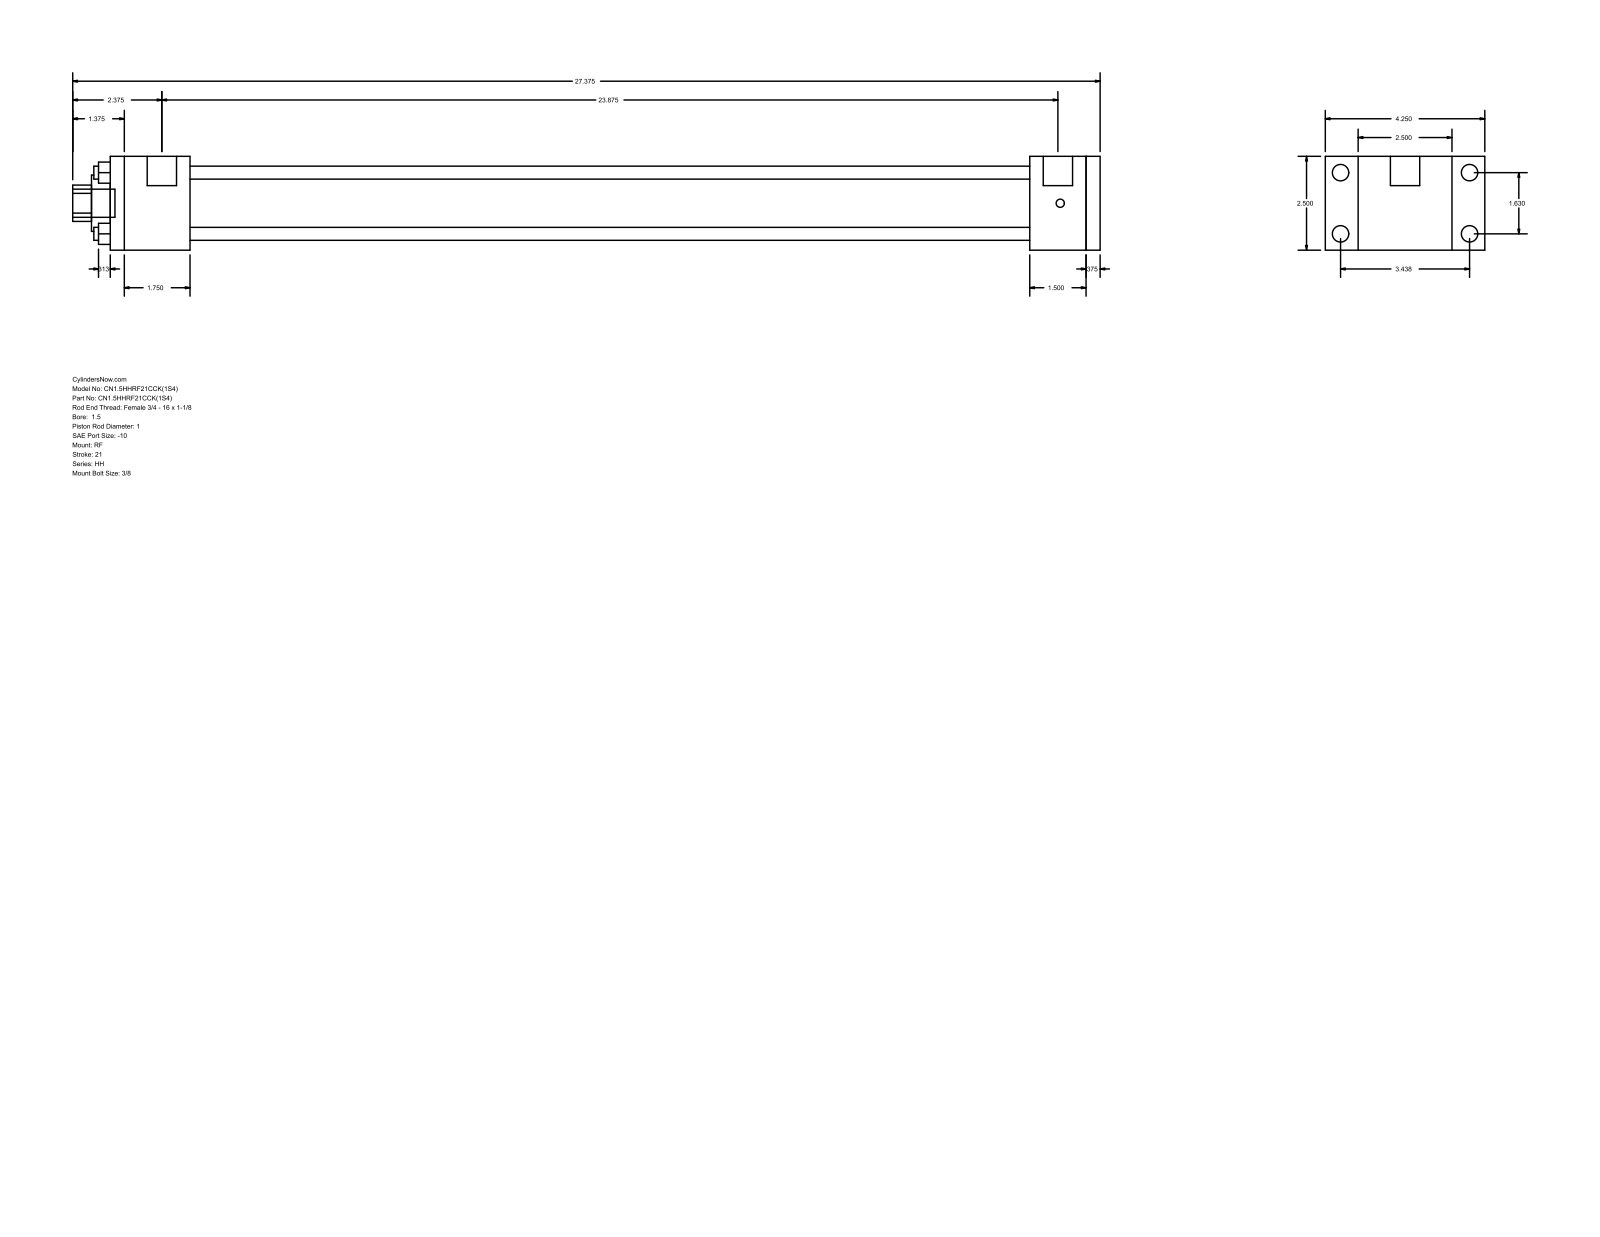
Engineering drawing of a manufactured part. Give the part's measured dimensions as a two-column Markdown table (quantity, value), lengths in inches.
| quantity | value |
| --- | --- |
| part name | HH_RF__0150_1 |
| STEP written by | GSSL Pune (CONFIG_CONTROL_DESIGN) |
| units | inches |
| bodies | 0 solids, 92 faces (64 planar, 28 cylindrical, 0 other) |
| overall size | 27.375 × 4.25 × 2.5 |
| round holes (diameter × count) | 0.345 × 4, 1 × 1, 1.5 × 1, 1.75 × 1 |
| round bosses / shafts (diameter × count) | 0.438 × 4, 0.219 × 4, 0.781 × 2, 0.75 × 1 |
| partial cylindrical surfaces (radius × count) | 0.484 × 1 |
| main face-to-face distances | 2.5, 0.375, 22.375, 23.875, 24.25, 1.5, 1.875, 2.125, 24.5, 26 |
| hole center spacings | 1.152, 1.63, 2.305 |
